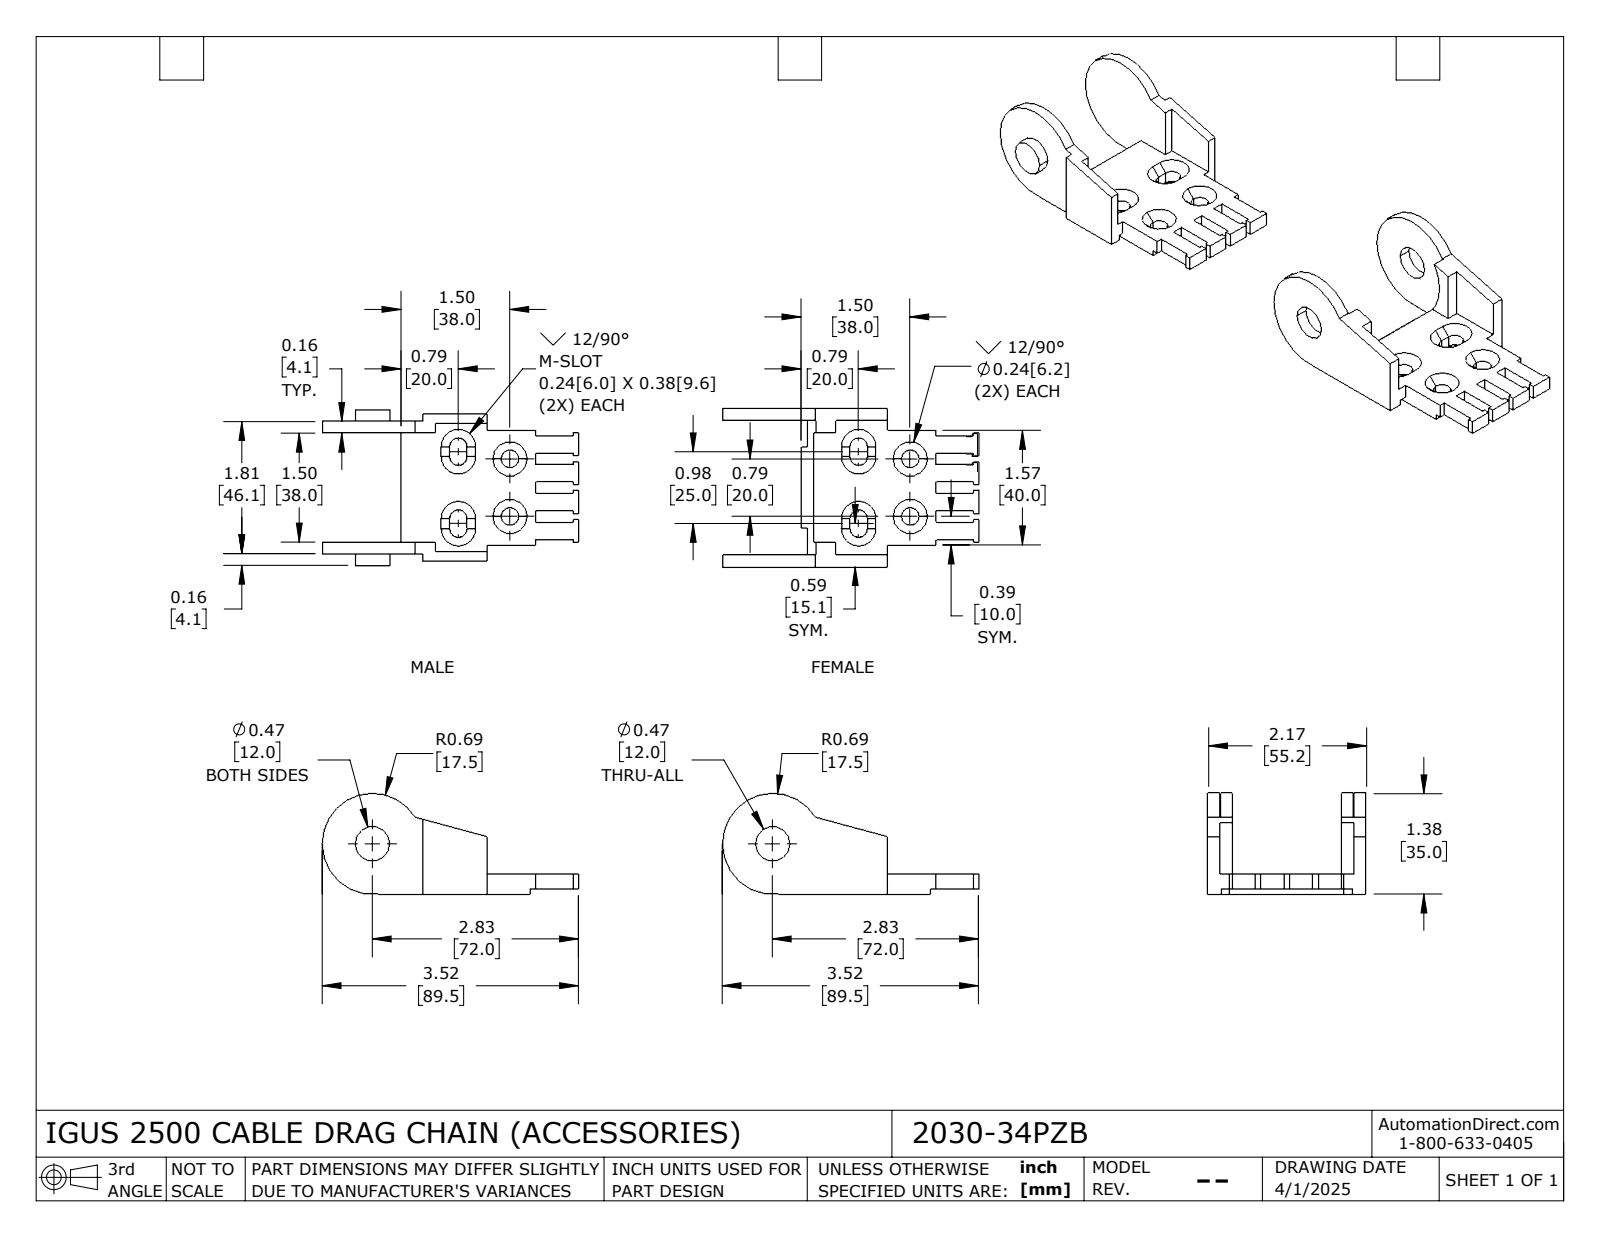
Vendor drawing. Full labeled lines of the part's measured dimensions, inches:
Part name (STEP PRODUCT): 2030-34PZB
STEP written by: SolidWorks 2024 (AUTOMOTIVE_DESIGN)
Units: inches
Bodies: 2 solids, 203 faces (152 planar, 35 cylindrical, 16 other)
Overall size (bounding box): 9.024 × 2.173 × 1.378
Volume: 3.304 in³ · Surface area: 44.35 in²
Round holes (diameter × count): ⌀0.244 ×4, ⌀0.472 ×1
Round bosses / shafts (diameter × count): ⌀0.472 ×1
Partial cylindrical surfaces — rounded edges, fillets, slot ends (radius × count): R0.12 ×8, R0.689 ×2, R0.697 ×1
Main face-to-face distances: 0.169, 0.276, 1.835, 1.665, 0.079, 0.339, 2.004, 0.179, 1.994, 1.825
Hole centre spacings: 0.787, 5.5, 5.556
